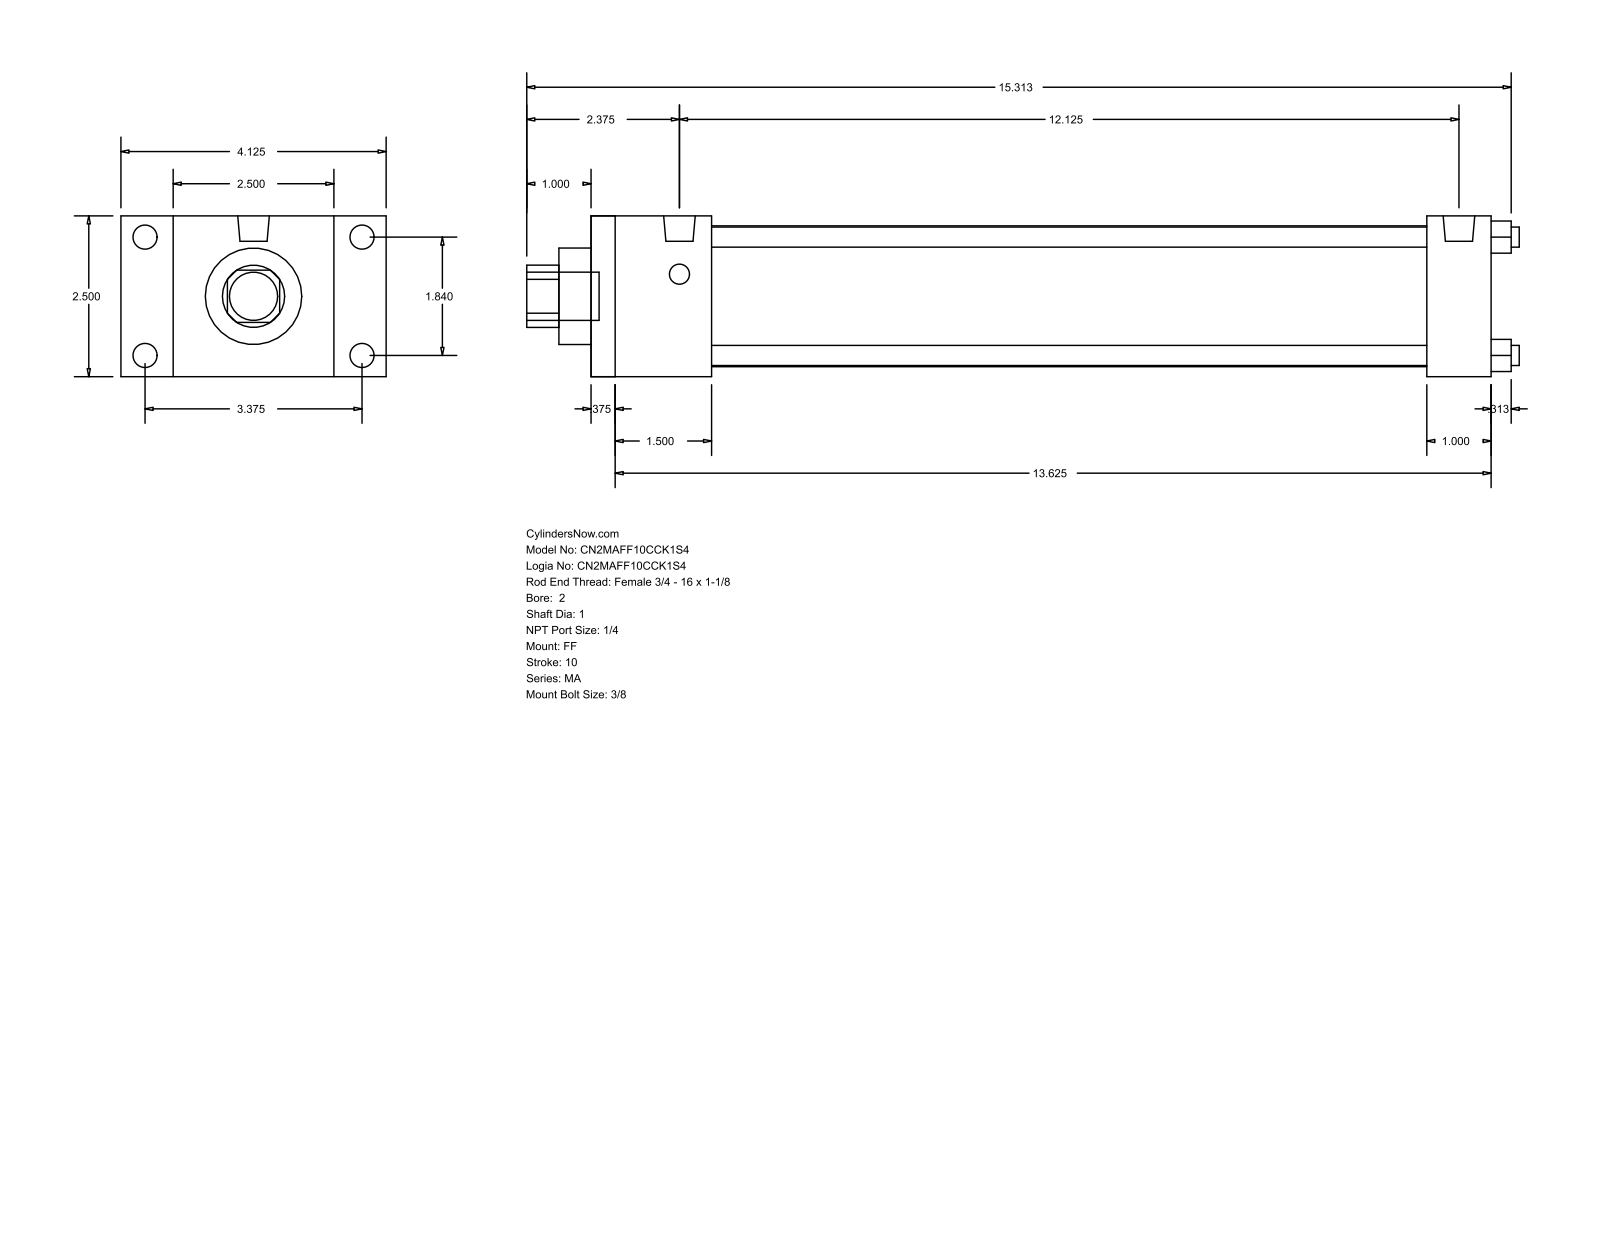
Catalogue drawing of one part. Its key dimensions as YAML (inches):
part_name: "MA_FF__0200_1"
step_written_by: "GSSL Pune (CONFIG_CONTROL_DESIGN)"
units: inches
bodies: {solids: 0, faces: 92, planar: 64, cylindrical: 28, other: 0}
overall_size: [15.437, 4.125, 2.5]
round_holes:
  - {diameter: 0.313, count: 4}
  - {diameter: 1, count: 1}
  - {diameter: 1.5, count: 1}
  - {diameter: 2.19, count: 1}
round_bosses_or_shafts:
  - {diameter: 0.375, count: 4}
  - {diameter: 0.313, count: 4}
  - {diameter: 0.492, count: 2}
  - {diameter: 0.75, count: 1}
partial_cylinders:
  - {radius: 0.484, count: 1}
face_to_face_distances: [2.5, 14, 0.375, 13.625, 1, 0.813, 0.5, 1.875, 13, 1.5]
hole_center_spacings: [1.301, 1.84, 2.602]
